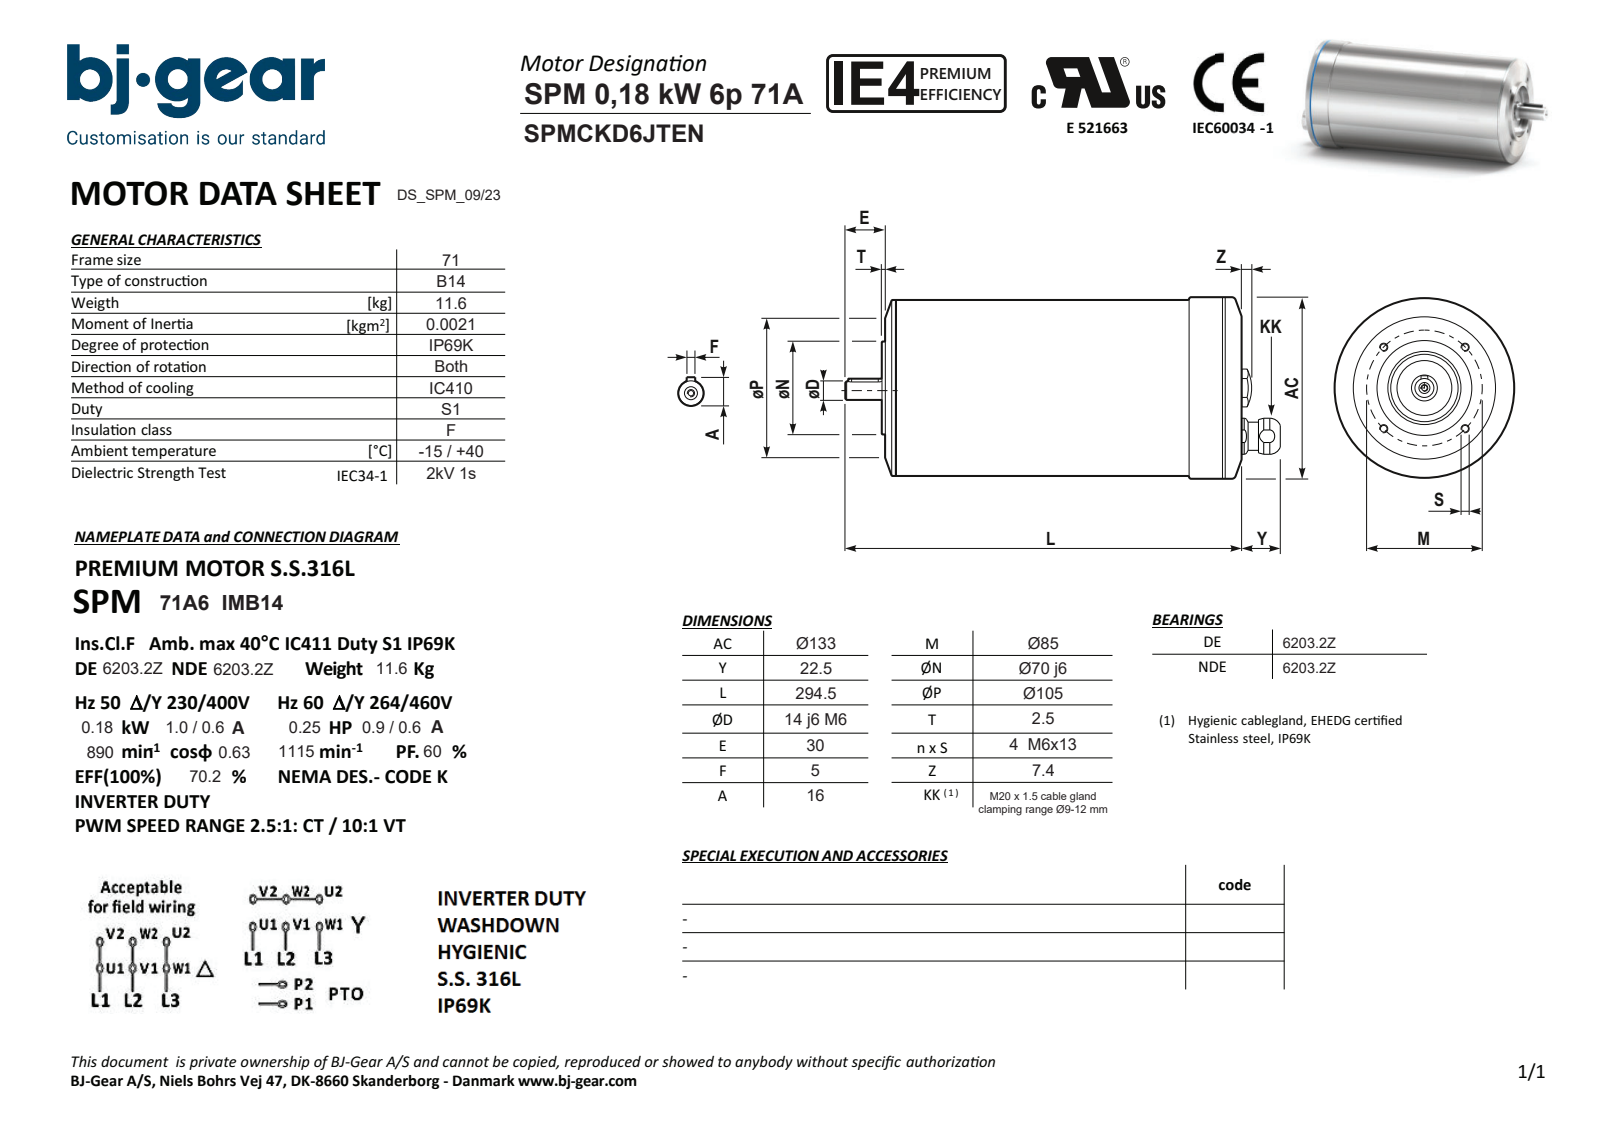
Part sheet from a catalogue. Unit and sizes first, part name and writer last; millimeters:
Units: millimetres
Overall size (bounding box): 322 × 133 × 133
Round holes (diameter × count): ⌀4.92 ×4, ⌀4.13 ×1, ⌀5.3 ×1, ⌀7 ×1, ⌀13.4 ×1, ⌀52 ×1, ⌀62 ×1
Round bosses / shafts (diameter × count): ⌀133 ×1, ⌀132.98 ×1, ⌀129 ×1, ⌀128.98 ×1, ⌀70 ×1, ⌀20 ×1, ⌀17 ×1, ⌀14 ×1
Partial cylindrical surfaces — rounded edges, fillets, slot ends (radius × count): R2.5 ×2, R12.8 ×1
Main face-to-face distances: 264.5, 259, 5.5, 263.5, 4.5, 1, 2.5, 8, 267, 3.5
Hole centre spacings: 42.5, 60.1, 30.31, 70.75, 84.99, 34
Volume: 3 471 000 mm³ · Surface area: 138 275 mm²
Bodies: 1 solid, 90 faces (31 planar, 33 cylindrical, 26 other)
Part name (STEP PRODUCT): SPMCKD6JTENN4KSA1-N---NNN
STEP written by: Solid Edge (AUTOMOTIVE_DESIGN)
